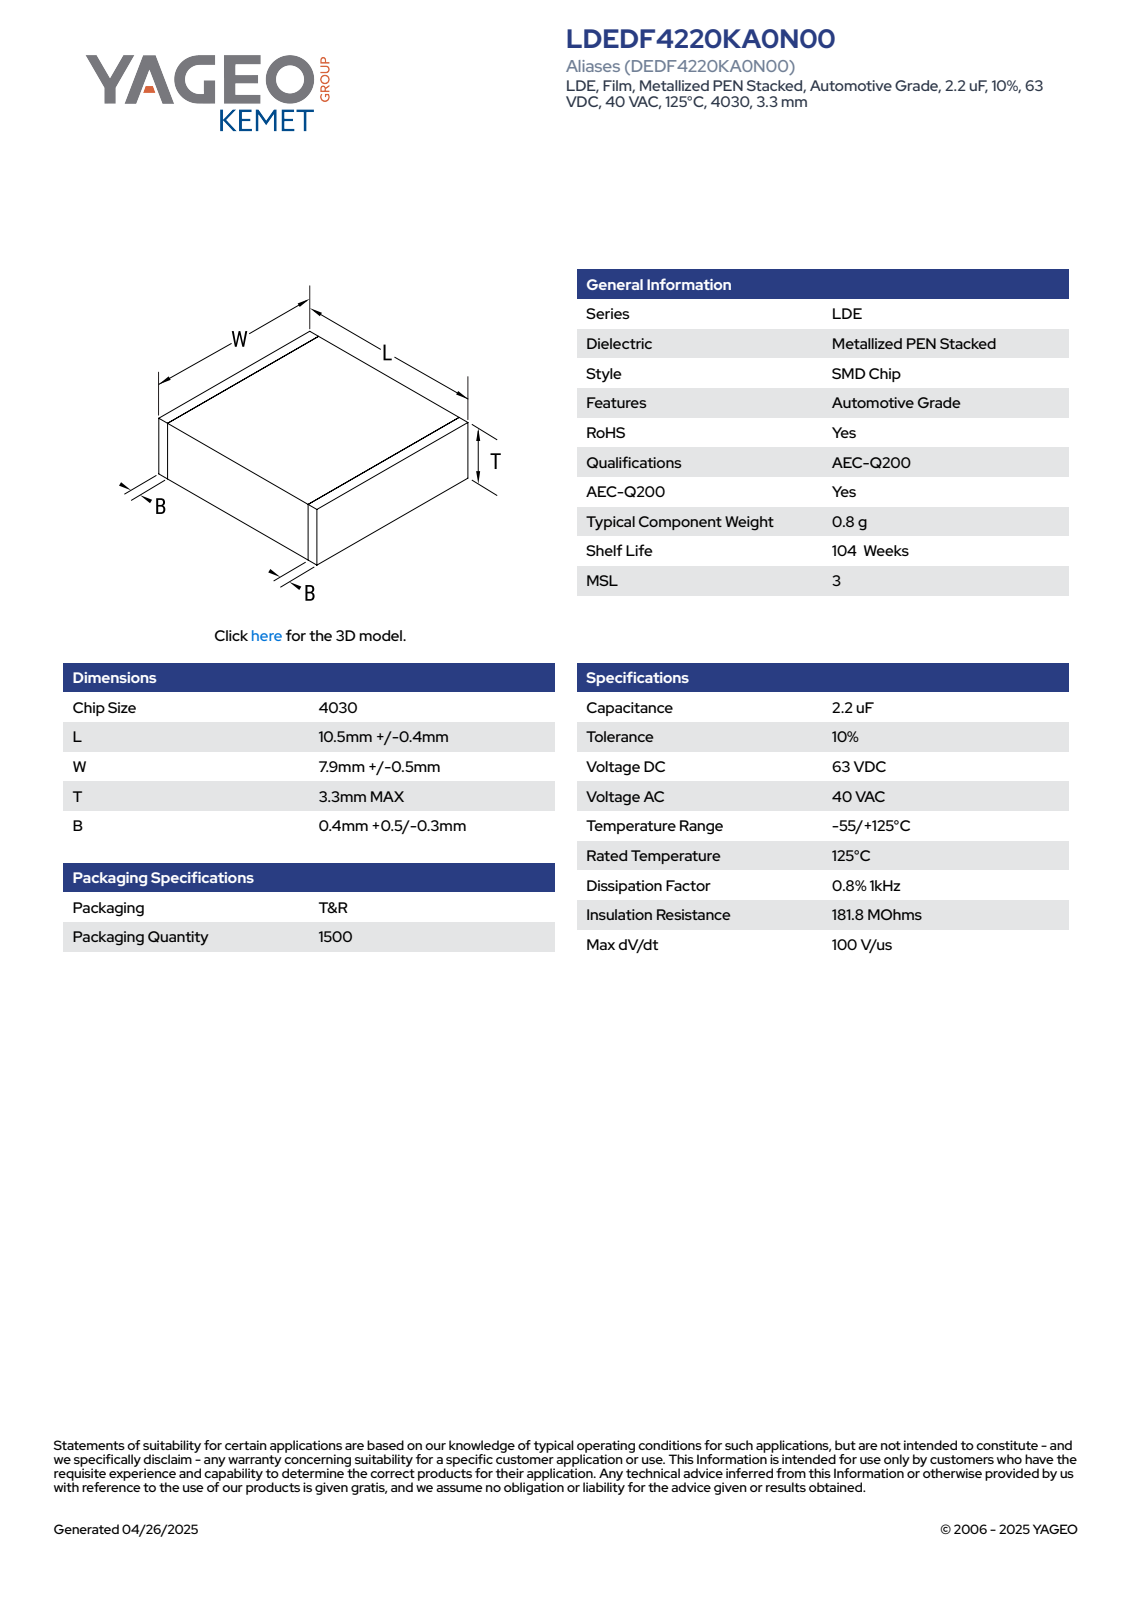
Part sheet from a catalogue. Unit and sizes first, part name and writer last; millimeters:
Units: millimetres
Overall size (bounding box): 10.9 × 8.4 × 3.3
Main face-to-face distances: 3.28, 8.38, 10.9, 3.29, 3.3, 8.39, 8.4, 0.5, 10.4, 9.9
Volume: 300 mm³ · Surface area: 316 mm²
Bodies: 4 solids, 73 faces (73 planar, 0 cylindrical, 0 other)
Part name (STEP PRODUCT): CFS_LDELDB_4030_L10.9W8.4T3.3B0.9
STEP written by: SolidWorks 2020 (AUTOMOTIVE_DESIGN)
